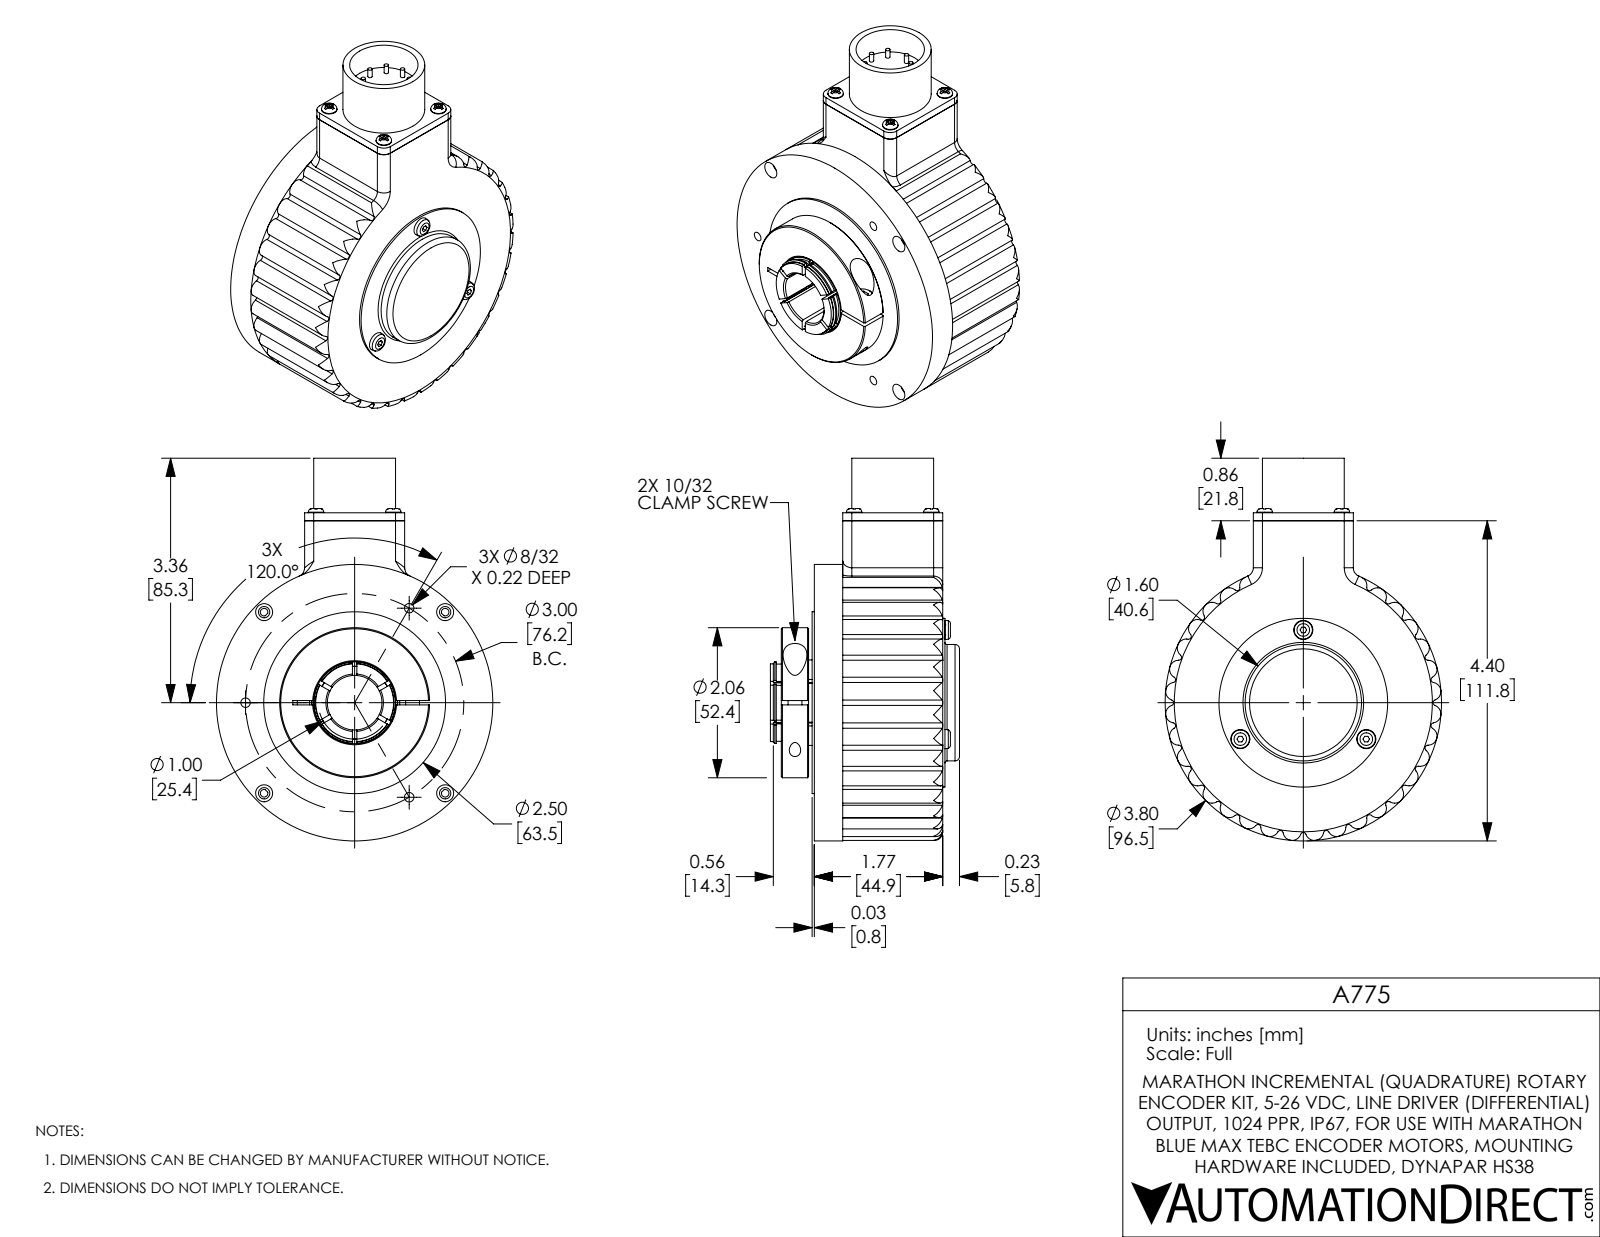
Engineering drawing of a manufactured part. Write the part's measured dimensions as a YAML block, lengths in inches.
part_name: "A775"
step_written_by: "SolidWorks 2017 (AUTOMOTIVE_DESIGN)"
units: inches
bodies: {solids: 5, faces: 691, planar: 270, cylindrical: 328, other: 93}
overall_size: [5.26, 3.8, 2.599]
volume: 28.5
surface_area: 162.3
round_holes:
  - {diameter: 0.156, count: 7}
  - {diameter: 0.085, count: 4}
  - {diameter: 0.104, count: 4}
  - {diameter: 0.12, count: 4}
  - {diameter: 0.234, count: 4}
  - {diameter: 0.13, count: 3}
  - {diameter: 0.156, count: 1}
  - {diameter: 0.201, count: 1}
  - {diameter: 0.328, count: 1}
  - {diameter: 0.751, count: 1}
  - {diameter: 0.94, count: 1}
  - {diameter: 1, count: 1}
round_bosses_or_shafts:
  - {diameter: 0.06, count: 8}
  - {diameter: 0.212, count: 4}
  - {diameter: 0.112, count: 4}
  - {diameter: 0.138, count: 3}
  - {diameter: 3.8, count: 1}
  - {diameter: 3.34, count: 1}
  - {diameter: 3.29, count: 1}
  - {diameter: 2.5, count: 1}
partial_cylinders:
  - {radius: 0.125, count: 38}
  - {radius: 0.039, count: 31}
  - {radius: 0.851, count: 1}
  - {radius: 1.715, count: 1}
face_to_face_distances: [1.375, 0.368, 1.007, 1.766, 1.398, 0.391, 0.03, 0.2, 0.453, 0.375]
hole_center_spacings: [1.76, 2.489, 0.807, 1, 1.5, 1.732, 2.419, 0.498]
